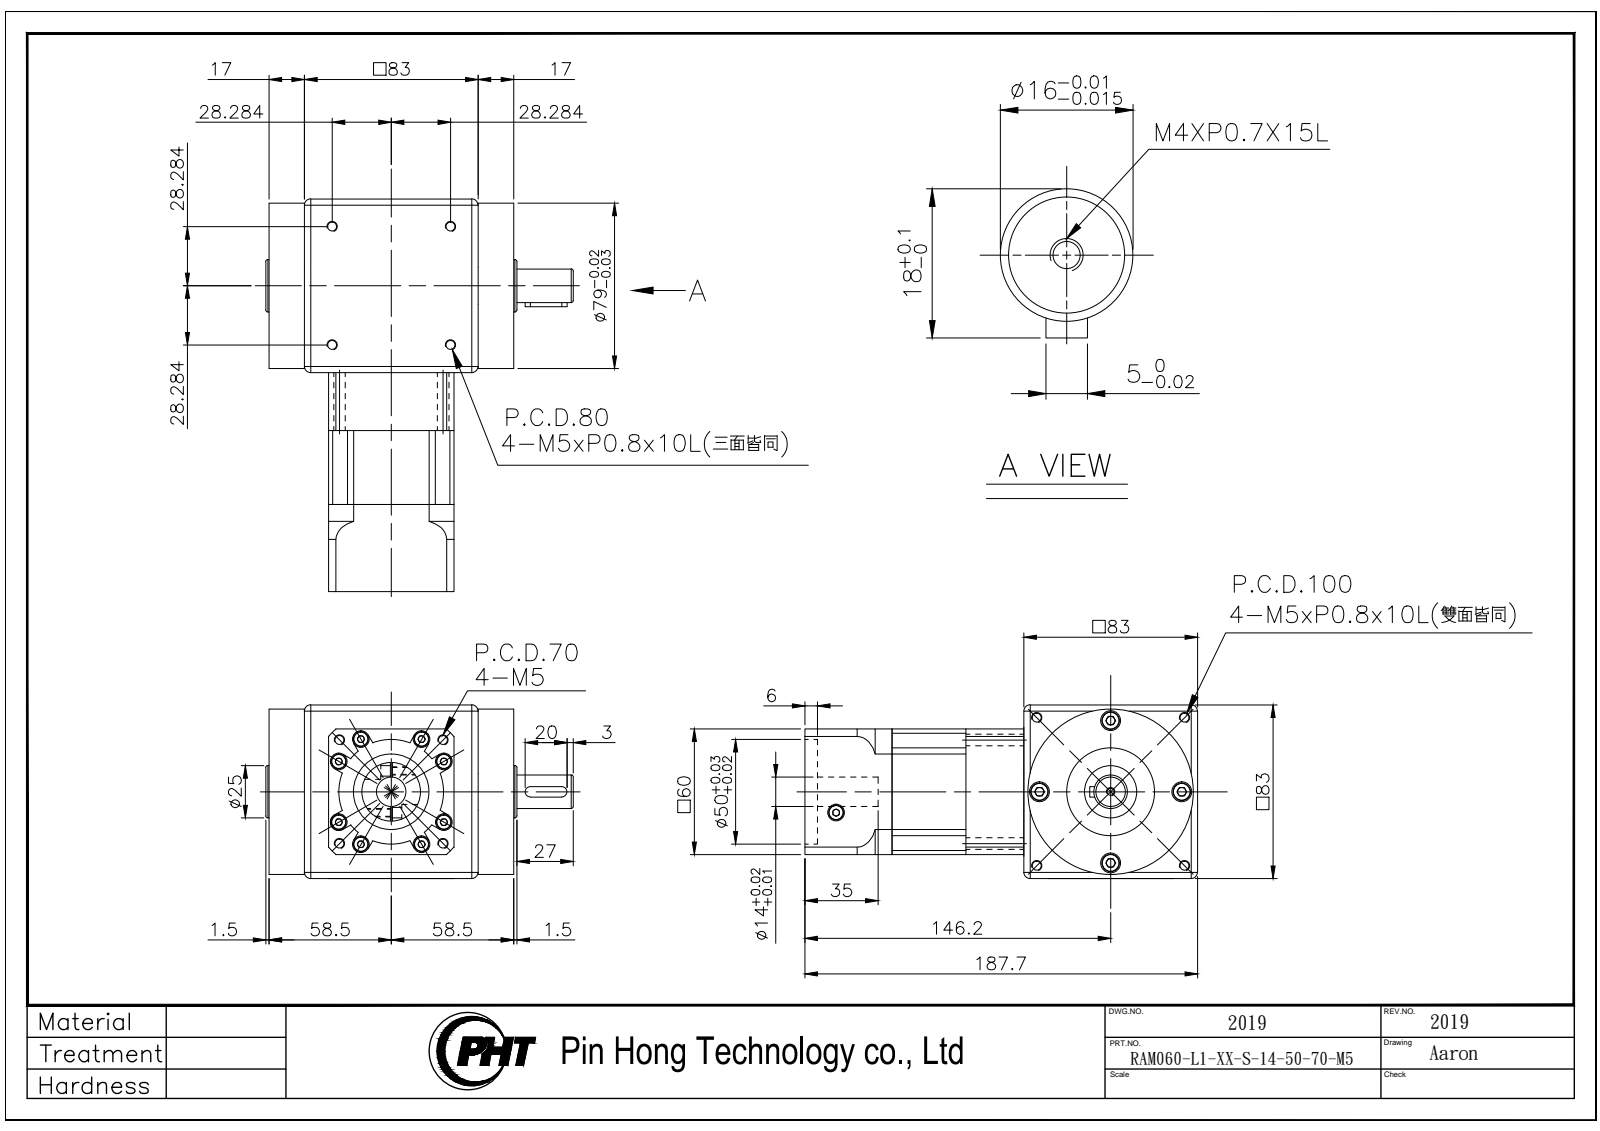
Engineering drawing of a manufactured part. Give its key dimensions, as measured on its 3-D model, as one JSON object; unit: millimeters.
{"part_name": "RAM060-L1-XX-S-14-50-70-M5_2019", "step_written_by": "SolidWorks 2016 (AUTOMOTIVE_DESIGN)", "units": "millimeters", "bodies": {"solids": 5, "faces": 687, "planar": 319, "cylindrical": 236, "other": 132}, "overall_size": [187.7, 147, 83], "volume_mm3": 1054000, "surface_area_mm2": 123493, "round_holes": [[4.2, 16], [8, 10], [4.5, 8], [5.5, 8], [9.5, 4], [3.3, 1], [4, 1], [14, 1], [36, 1]], "round_bosses_or_shafts": [[8.5, 8], [7, 8], [79, 1], [55, 1], [42, 1], [28, 1], [25, 1], [16, 1]], "partial_cylinders_radius": [[5, 4], [2.5, 2], [25, 1], [35, 1], [40, 1], [57.15, 1]], "face_to_face_distances": [83, 11.5, 71.5, 60, 27.7, 35.35, 63.05, 28.5, 88.5, 146.05], "hole_center_spacings": [29, 10.26, 14.14, 39.25, 41.01, 42.9, 50.9, 53.15]}
